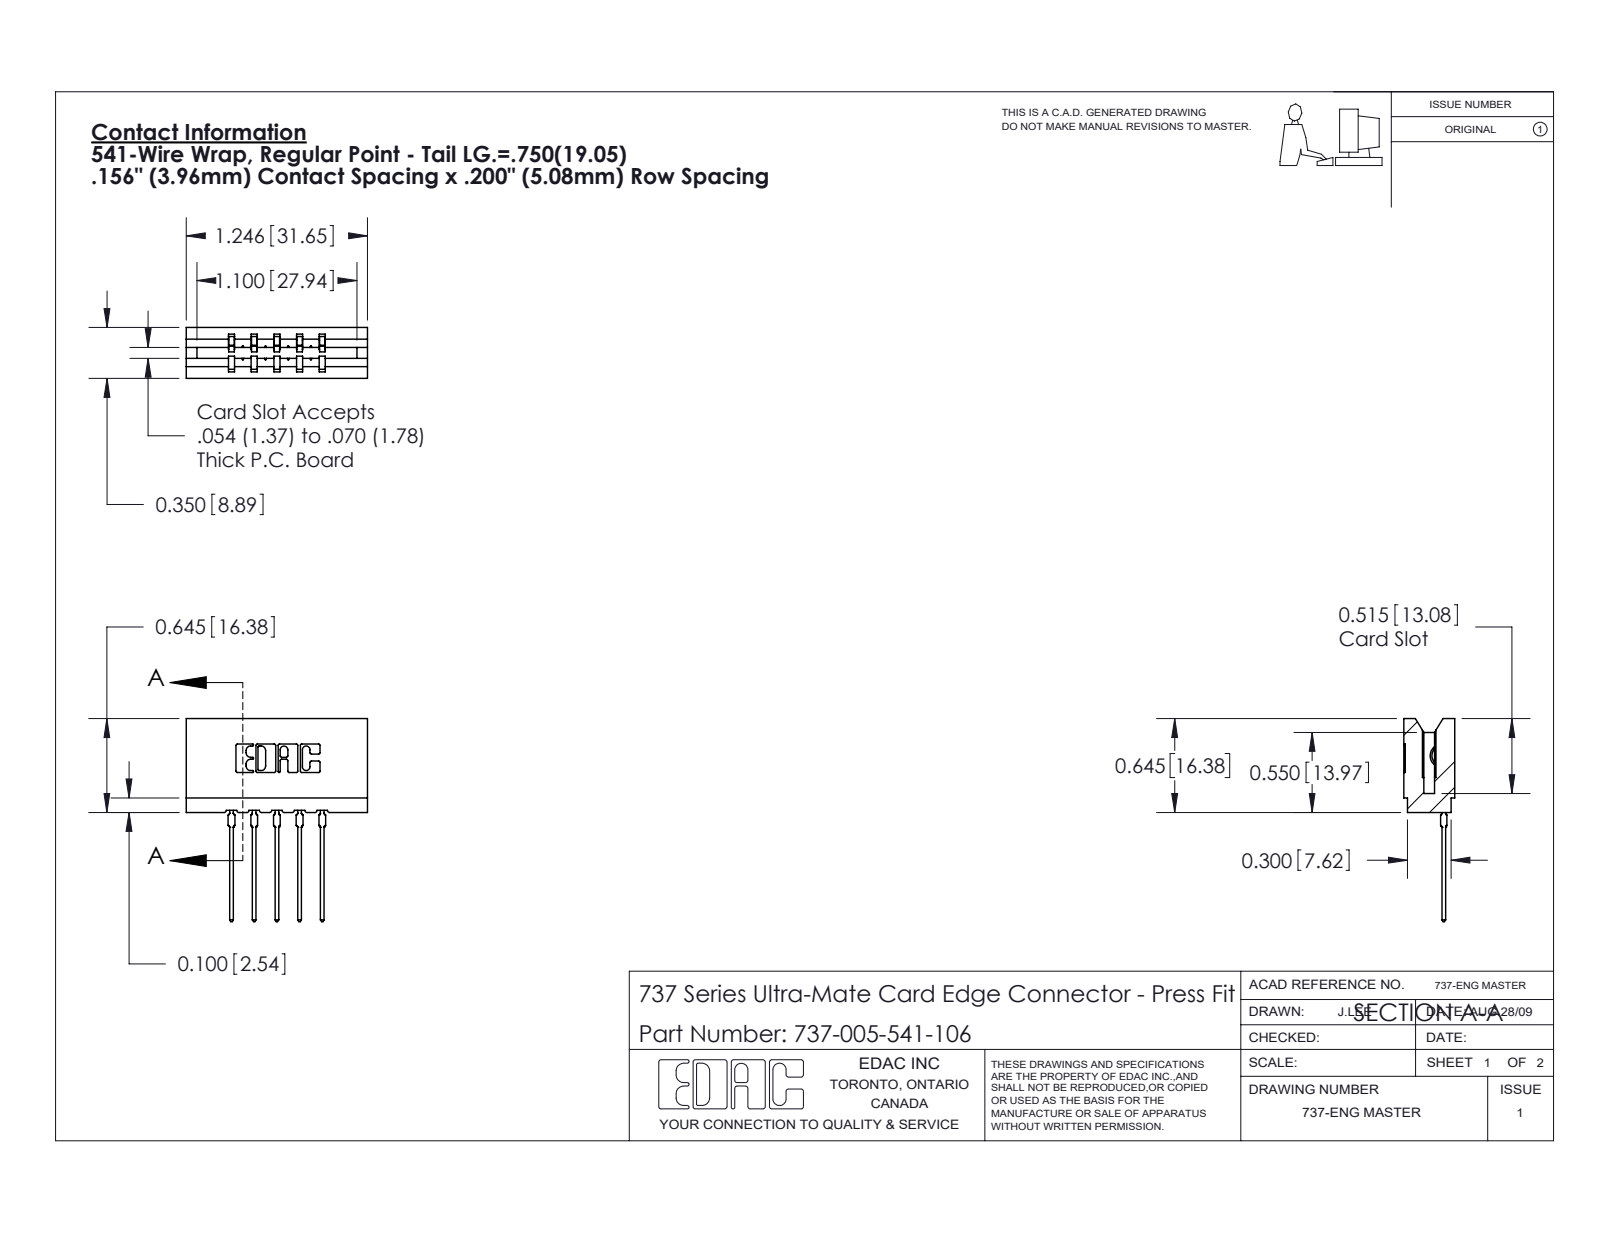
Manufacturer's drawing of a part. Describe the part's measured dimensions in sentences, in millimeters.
The part is named "737 Part_Insulator Option - 06; 745-292-001_541; 737-005-541-106". Its 3-D file was written by "SolidWorks 2020 (CONFIG_CONTROL_DESIGN)". It is 6 solids with 660 faces: 395 planar, 135 cylindrical and 130 other. Overall it measures 35.5 by 31.6 by 8.9 millimeters. Its volume is 3 330 cubic millimeters and its surface area 3 888 square millimeters. Partial cylindrical surfaces (rounded edges, fillets, slot ends): 22 of radius 0.3, 10 of radius 0.4, 10 of radius 0.5, 6 of radius 0.2, 6 of radius 0.8, 4 of radius 0.1, 4 of radius 0.3, 3 of radius 0.7. The main face-to-face distances are 3.5, 5.4, 4, 8.9, 7.9, 5, 1.9, 9, 1.1, 0.6.
